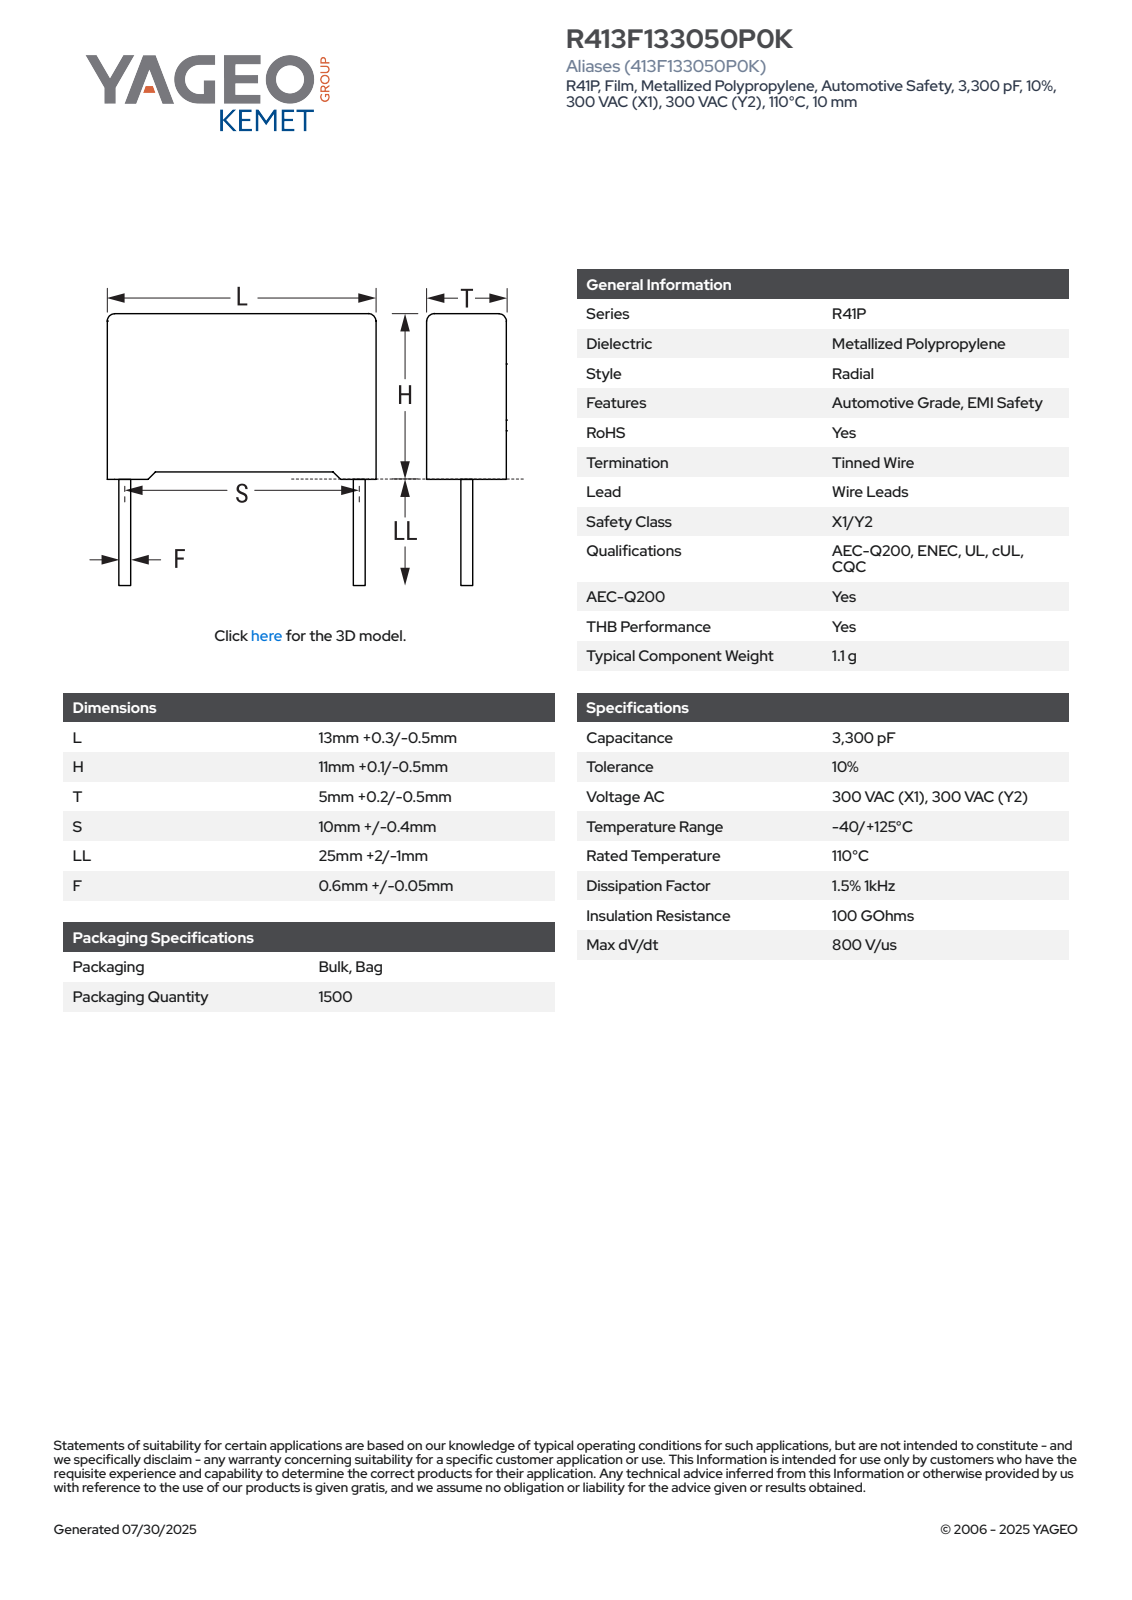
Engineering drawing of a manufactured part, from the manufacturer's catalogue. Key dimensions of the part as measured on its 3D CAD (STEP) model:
Part name (STEP PRODUCT): CFR_RB2_13X11X5_L13.3H11.1T5.2S10LL27F0.65
STEP written by: SolidWorks 2021 (AUTOMOTIVE_DESIGN)
Units: millimetres
Bodies: 4 solids, 85 faces (77 planar, 8 cylindrical, 0 other)
Overall size (bounding box): 38.1 × 13.3 × 5.21
Volume: 742 mm³ · Surface area: 683 mm²
Round bosses / shafts (diameter × count): ⌀0.65 ×2
Partial cylindrical surfaces — rounded edges, fillets, slot ends (radius × count): R0.5 ×4
Main face-to-face distances: 5.2, 13.3, 10.35, 0.44, 4.76, 0.75, 11.1, 4.32, 12.86, 0.37
